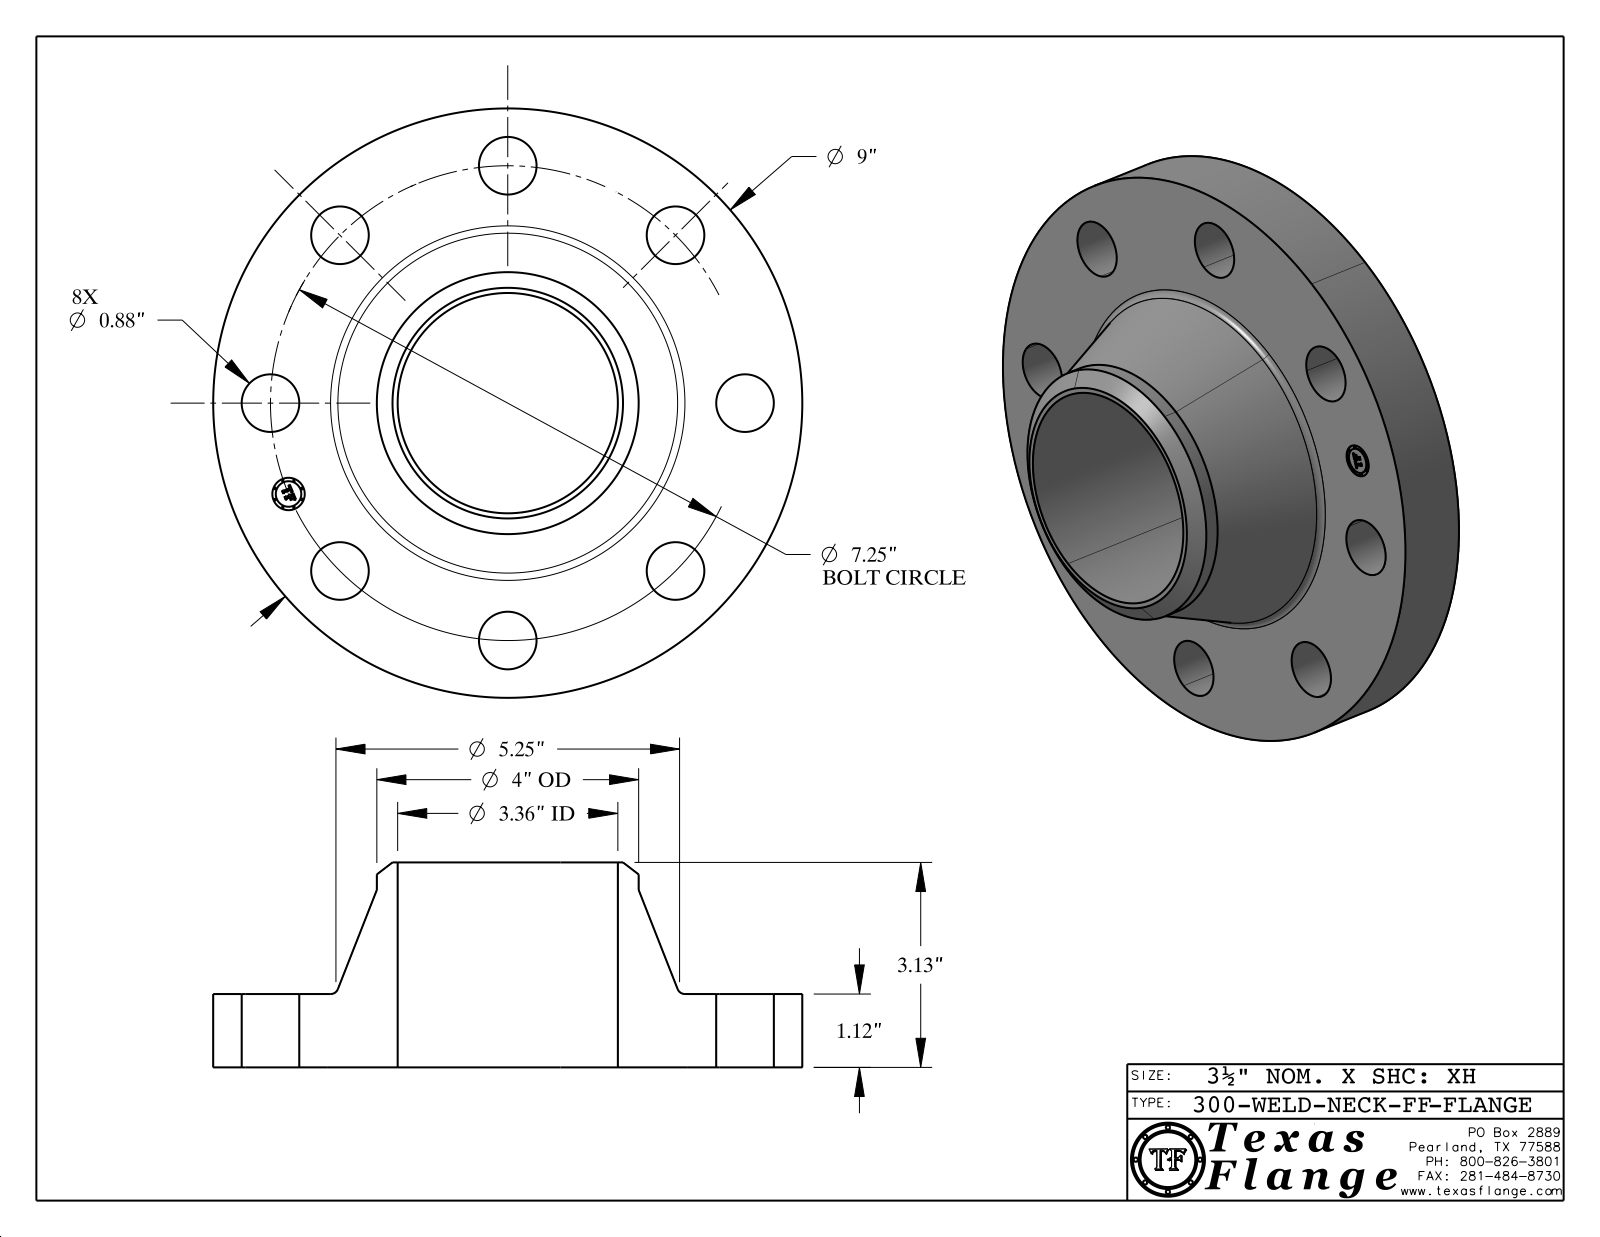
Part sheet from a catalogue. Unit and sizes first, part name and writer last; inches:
Units: inches
Overall size (bounding box): 9 × 9 × 3.13
Round holes (diameter × count): ⌀0.88 ×8, ⌀0.495 ×1, ⌀3.364 ×1
Round bosses / shafts (diameter × count): ⌀0.03 ×8, ⌀9 ×1, ⌀4 ×1, ⌀0.39 ×1
Main face-to-face distances: 1.12, 3.13, 2.01, 1.105, 0.015, 2.025, 0.148, 0.144, 0.027, 0.096
Hole centre spacings: 3.625, 2.774, 5.127, 6.698, 7.25, 1.415, 7.111, 4.028
Volume: 69.89 in³ · Surface area: 208.5 in²
Bodies: 1 solid, 417 faces (369 planar, 42 cylindrical, 6 other)
Part name (STEP PRODUCT): 300-WELD-NECK-FF
STEP written by: CATIA V5 STEP AP214 (AUTOMOTIVE_DESIGN)
